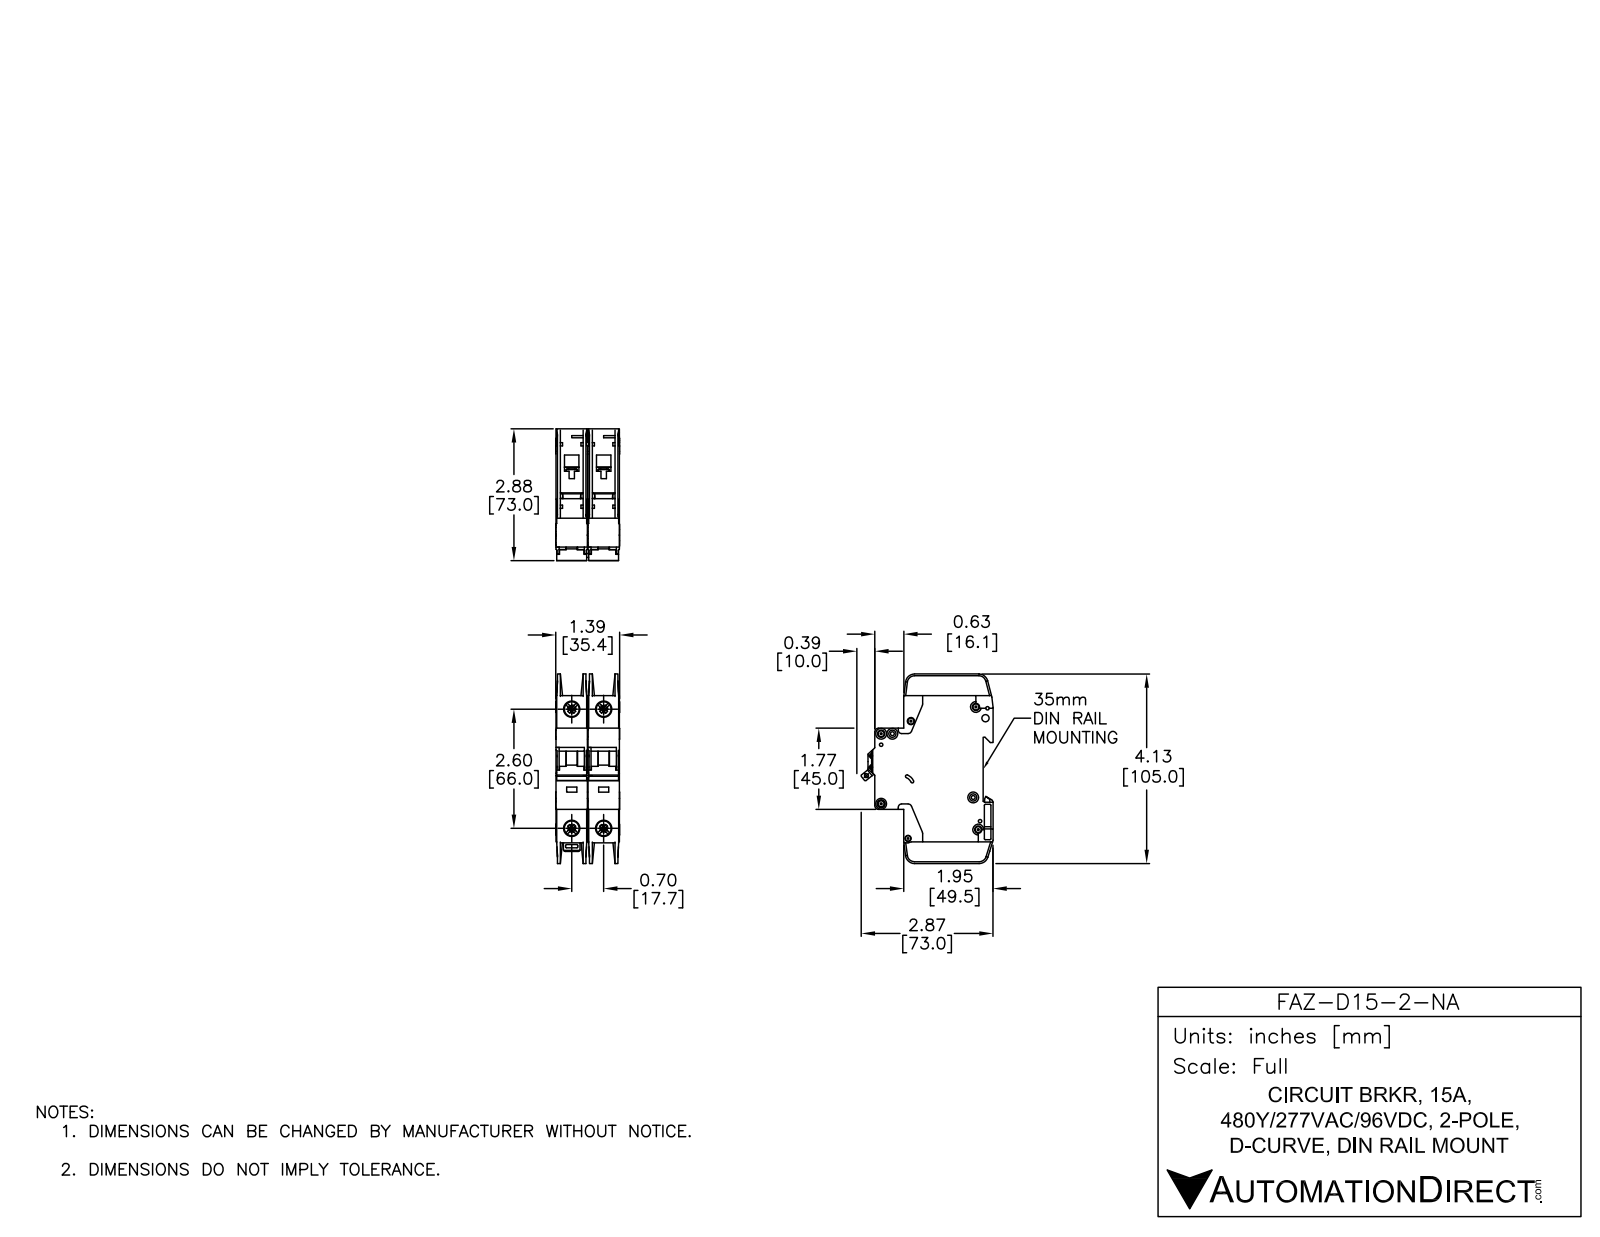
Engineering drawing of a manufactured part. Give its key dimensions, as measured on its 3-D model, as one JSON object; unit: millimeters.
{"part_name": "FAZ-D15-2-NA", "step_written_by": "SolidWorks 2014 (AUTOMOTIVE_DESIGN)", "units": "millimeters", "bodies": {"solids": 6, "faces": 1568, "planar": 818, "cylindrical": 526, "other": 224}, "overall_size": [105, 73.04, 35.4], "volume_mm3": 155390, "surface_area_mm2": 49479, "round_holes": [[3.6, 7], [7.15, 4], [8.2, 4], [1.09, 2], [1.5, 2], [4, 2], [1.9, 1], [2.15, 1], [2.2, 1], [2.55, 1], [3.3, 1], [3.4, 1]], "round_bosses_or_shafts": [[6, 7], [2.5, 2]], "partial_cylinders_radius": [[0.25, 47], [0.5, 24], [1, 18], [2, 12], [5, 5], [1.8, 4], [4, 4], [0.2, 2]], "face_to_face_distances": [17.7, 17.5, 0.7, 15.05, 2.45, 1.75, 15.75, 13.3, 35.2, 17], "hole_center_spacings": [6.2, 17.7, 66, 68.33, 5.19, 6.1, 8.19, 8.56]}
